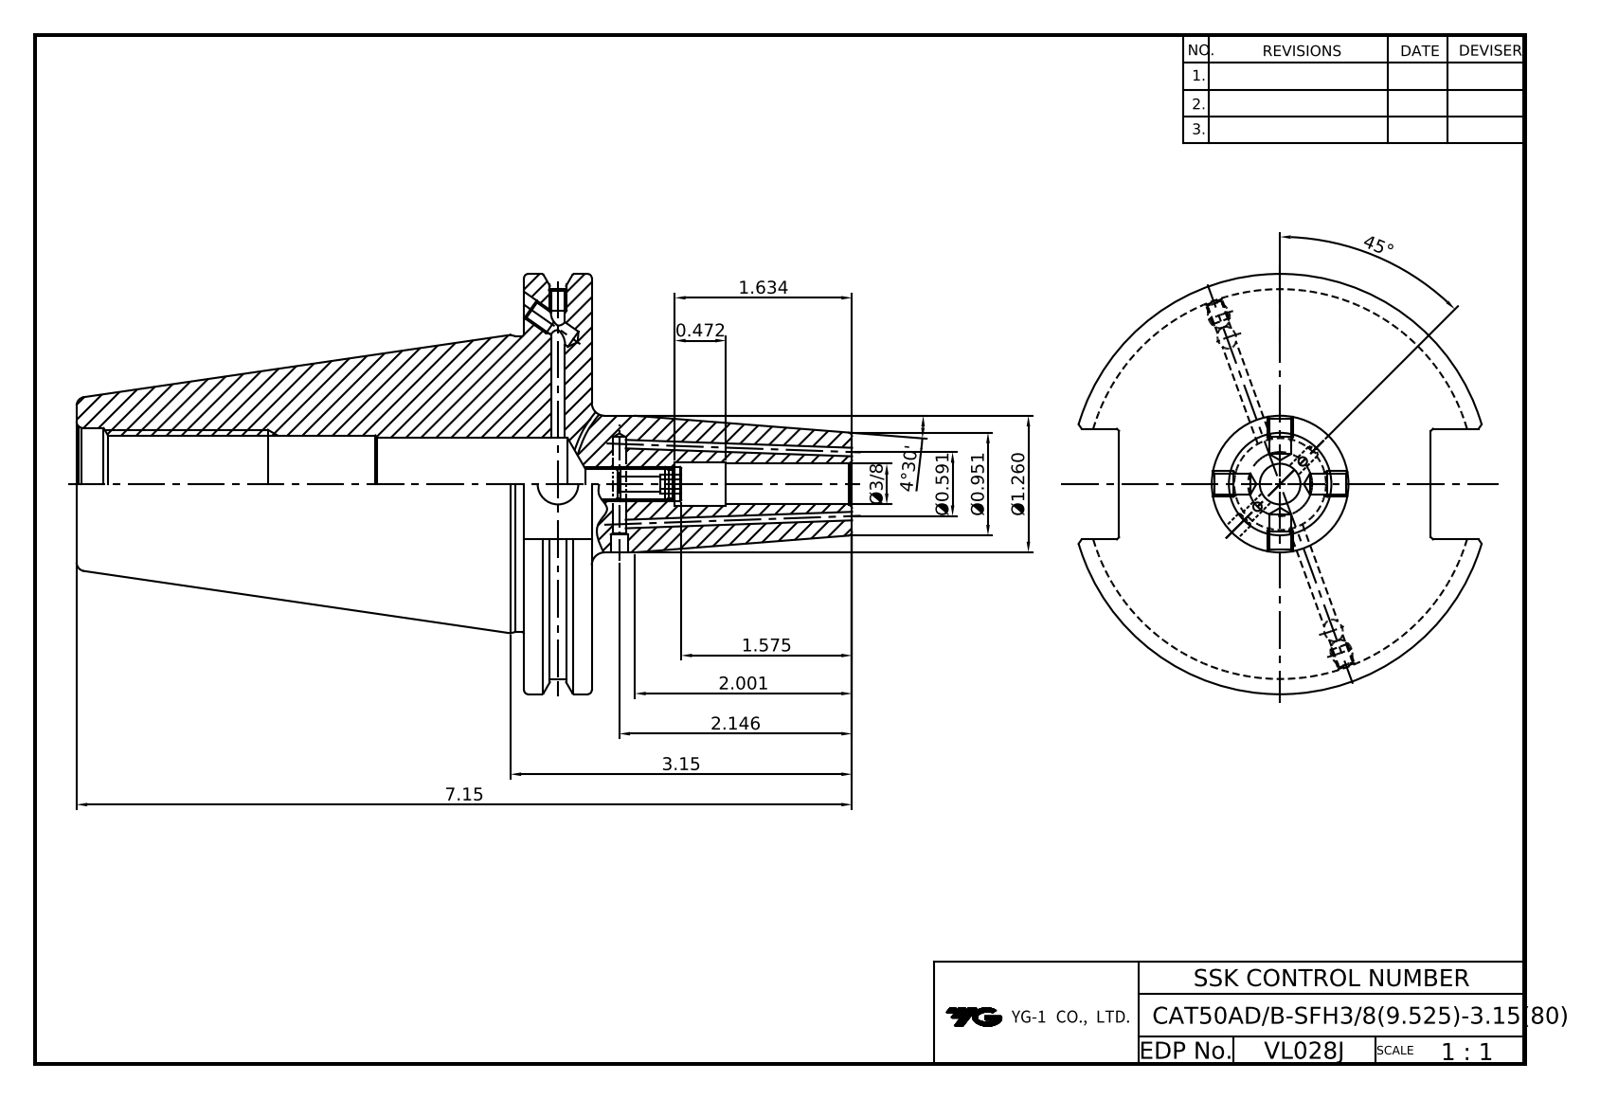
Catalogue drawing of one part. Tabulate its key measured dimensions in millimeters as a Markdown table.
| quantity | value |
| --- | --- |
| part name | LO-CAT50ADB-SFH9.525C-80 |
| STEP written by | Autodesk Inventor 2024 (AUTOMOTIVE_DESIGN) |
| units | millimeters |
| bodies | 1 solid, 90 faces (39 planar, 29 cylindrical, 22 other) |
| overall size | 181.6 × 98.42 × 94.69 |
| volume | 355 320 mm³ |
| surface area | 52 401 mm² |
| round holes (diameter × count) | 2.5 × 2, 3.24 × 2, 4.13 × 2, 4.2 × 2, 5 × 2, 9.53 × 2, 6.92 × 1, 10.72 × 1, 21.5 × 1, 21.97 × 1, 26.2 × 1 |
| round bosses / shafts (diameter × count) | 98.42 × 1, 91.29 × 1, 69.25 × 1, 32 × 1 |
| main face-to-face distances | 15.88, 104.77, 120.65, 73.03, 25.9, 181.6, 76.83, 60.95, 110.82, 6.05 |
